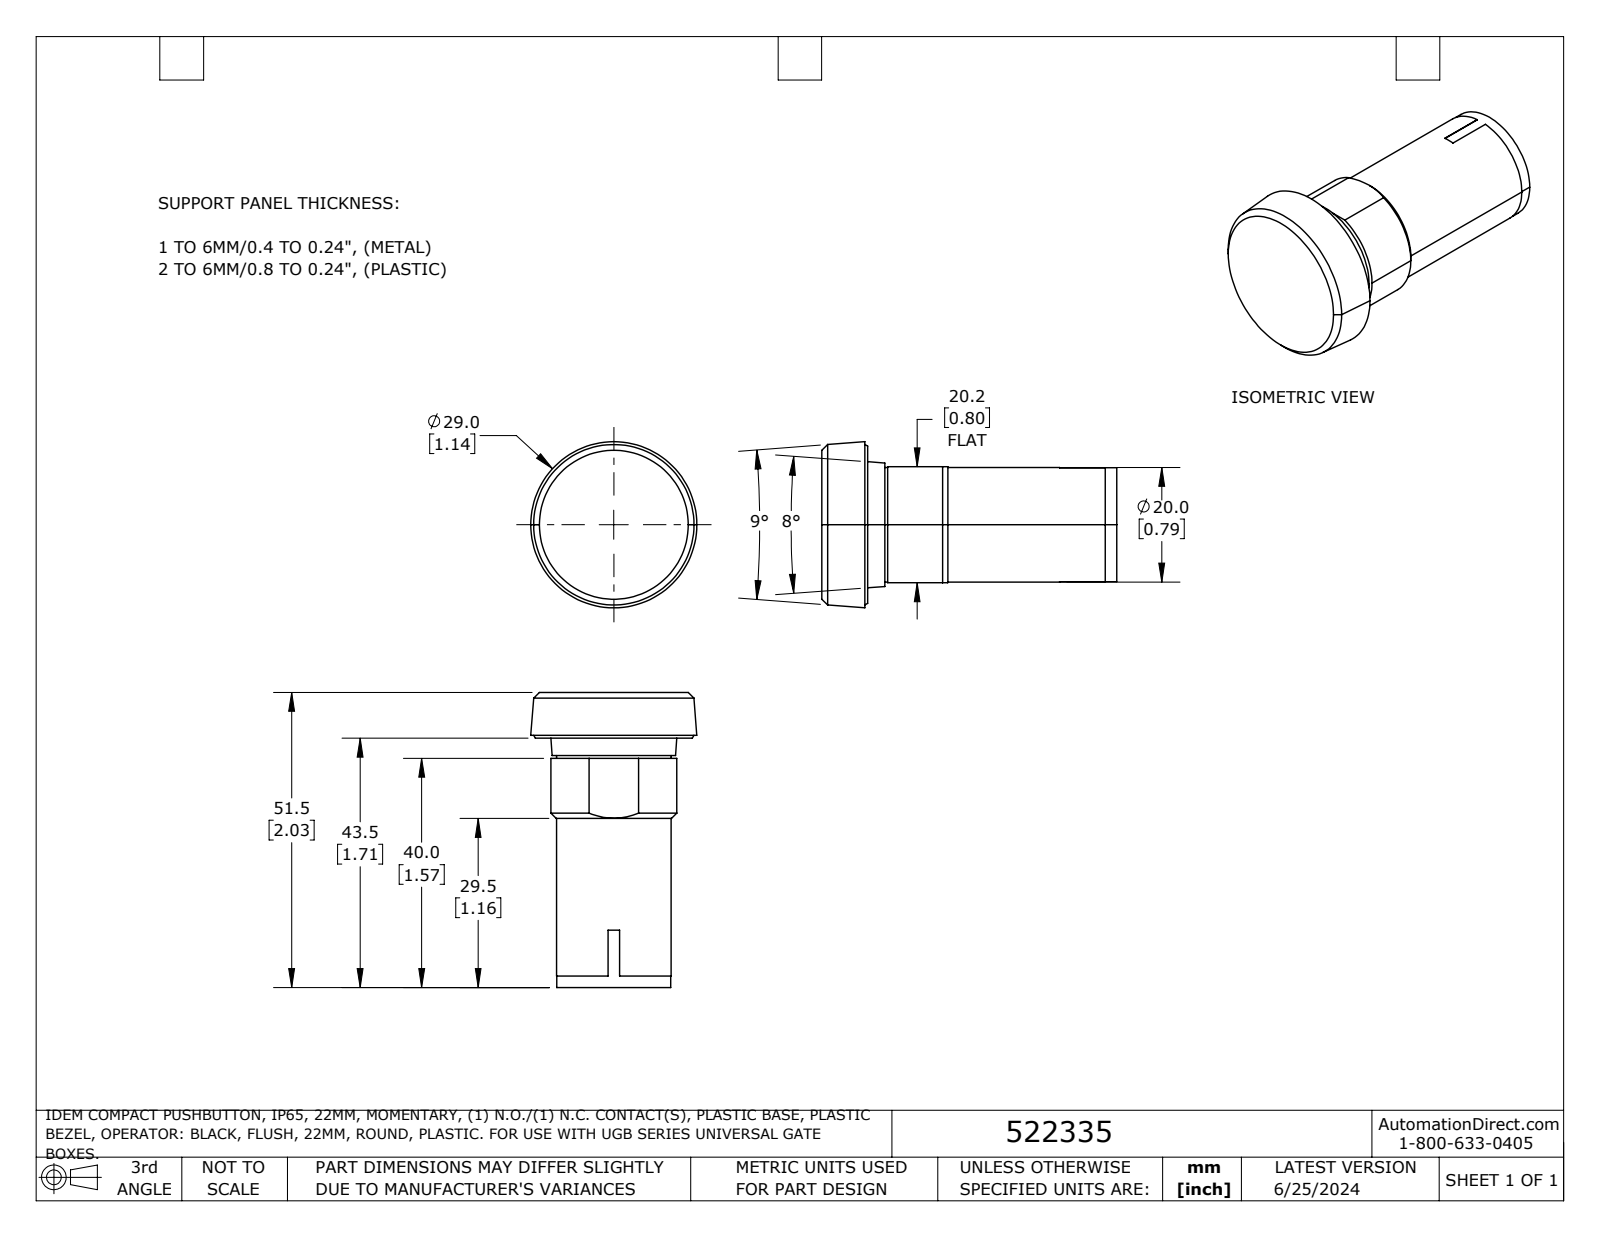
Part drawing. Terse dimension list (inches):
name: 522335
written by: SolidWorks 2023 (AUTOMOTIVE_DESIGN)
unit: in
bodies: 1 solid, 37 faces (17 planar, 10 cylindrical, 10 other)
size: 2.028 × 1.142 × 1.142
volume: 1.185 in³; area: 7.436 in²
bosses: 1× ⌀0.787, 1× ⌀0.783
rounds: 1× R0.433
face distances: 2.028, 0.315, 1.713, 0.138, 0.02, 0.797, 0.433, 0.453, 1.575, 0.118
